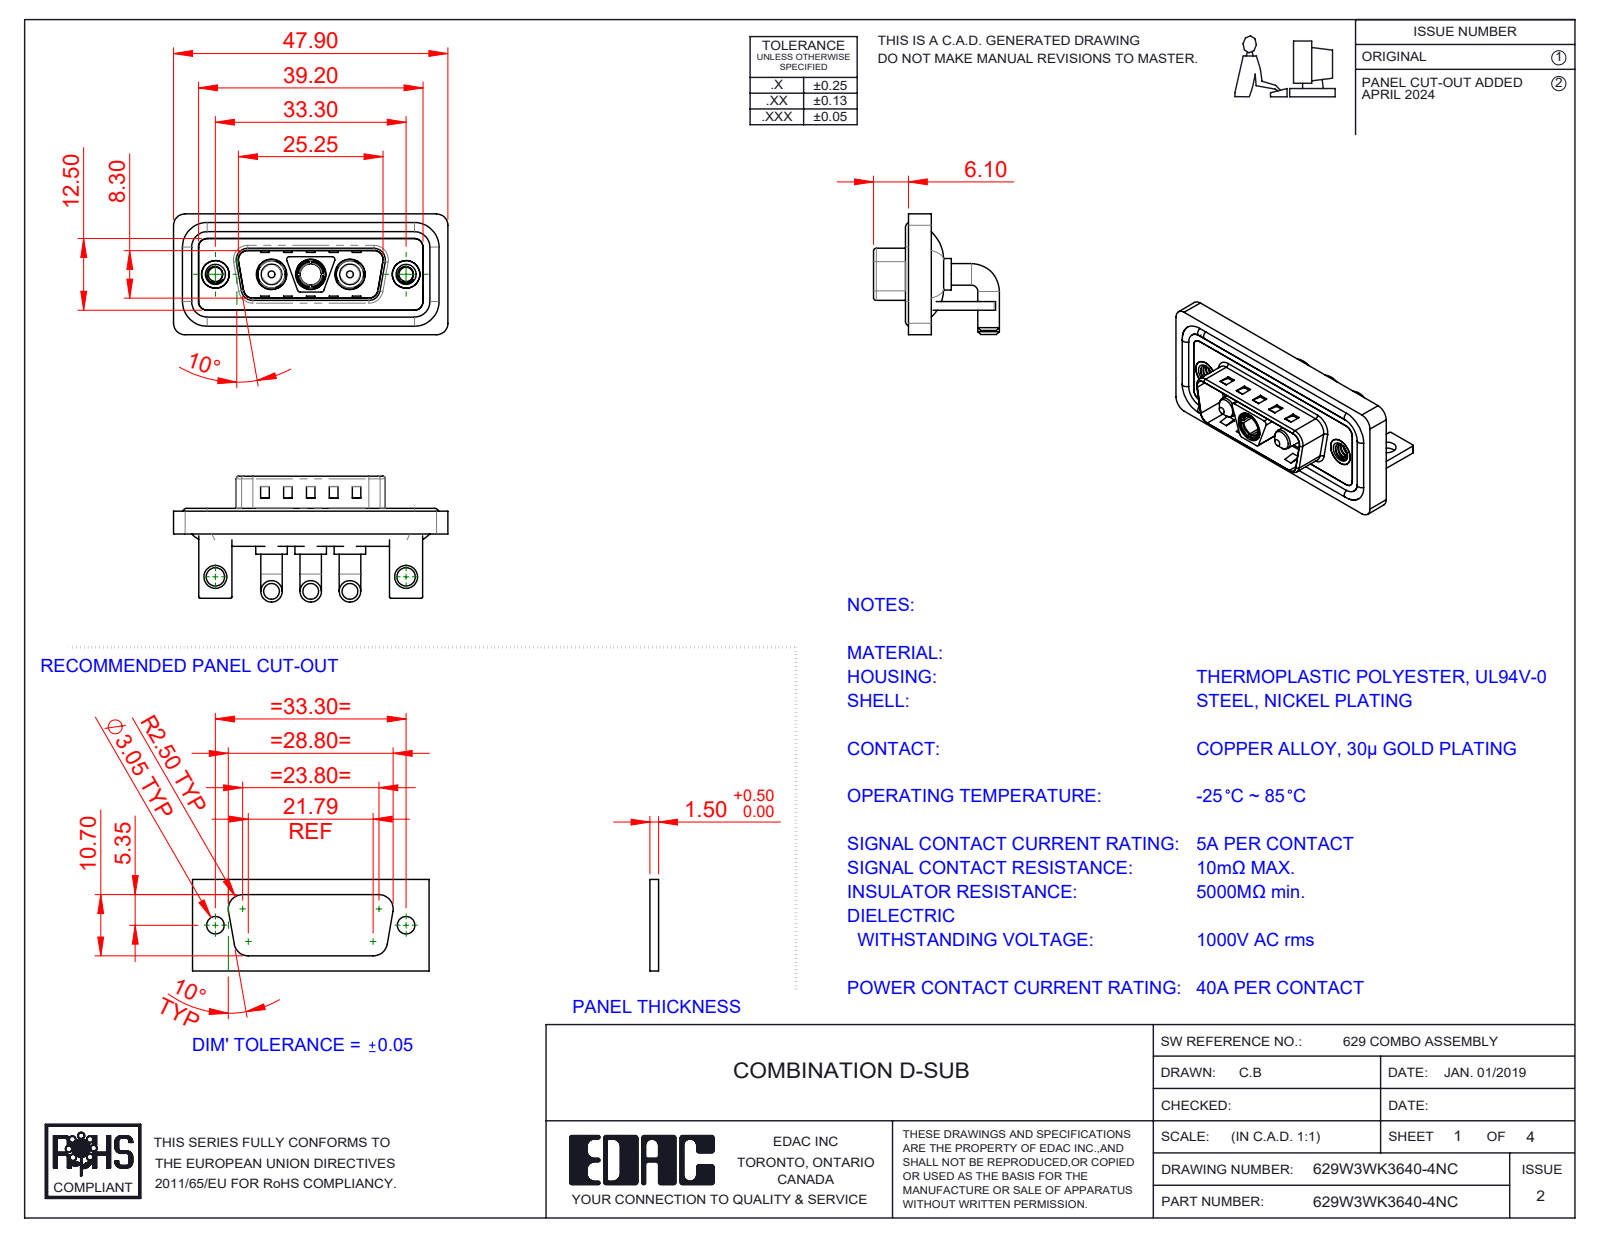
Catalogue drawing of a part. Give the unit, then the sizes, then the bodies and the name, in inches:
Units: inches
Overall size (bounding box): 1.886 × 0.865 × 0.831
Round holes (diameter × count): ⌀0.191 ×3, ⌀0.209 ×3, ⌀0.098 ×2, ⌀0.126 ×2, ⌀0.157 ×2, ⌀0.189 ×2, ⌀0.197 ×2, ⌀0.146 ×1
Round bosses / shafts (diameter × count): ⌀0.148 ×6, ⌀0.063 ×4, ⌀0.217 ×3, ⌀0.205 ×3, ⌀0.187 ×3, ⌀0.193 ×2, ⌀0.142 ×2, ⌀0.195 ×1
Partial cylindrical surfaces — rounded edges, fillets, slot ends (radius × count): R0.079 ×21, R0.059 ×18, R0.01 ×16, R0.02 ×13, R0.063 ×8, R0.024 ×4, R0.026 ×4, R0.035 ×4
Main face-to-face distances: 0.016, 0.059, 0.031, 0.114, 0.043, 0.083, 0.146, 0.063, 0.047, 0.177
Hole centre spacings: 0.27, 0.386, 0.656, 0.925, 1.311, 0.539
Volume: 0.389 in³ · Surface area: 15.71 in²
Bodies: 15 solids, 659 faces (251 planar, 274 cylindrical, 134 other)
Part name (STEP PRODUCT): 629Combo Shell Front_15 Contacts; 629Combo Waterproof Housing_15 Contacts; 629Combo Housing_3WK3; 629Combo Threaded Rivet_B (+5 more)
STEP written by: SolidWorks 2023 (CONFIG_CONTROL_DESIGN)
